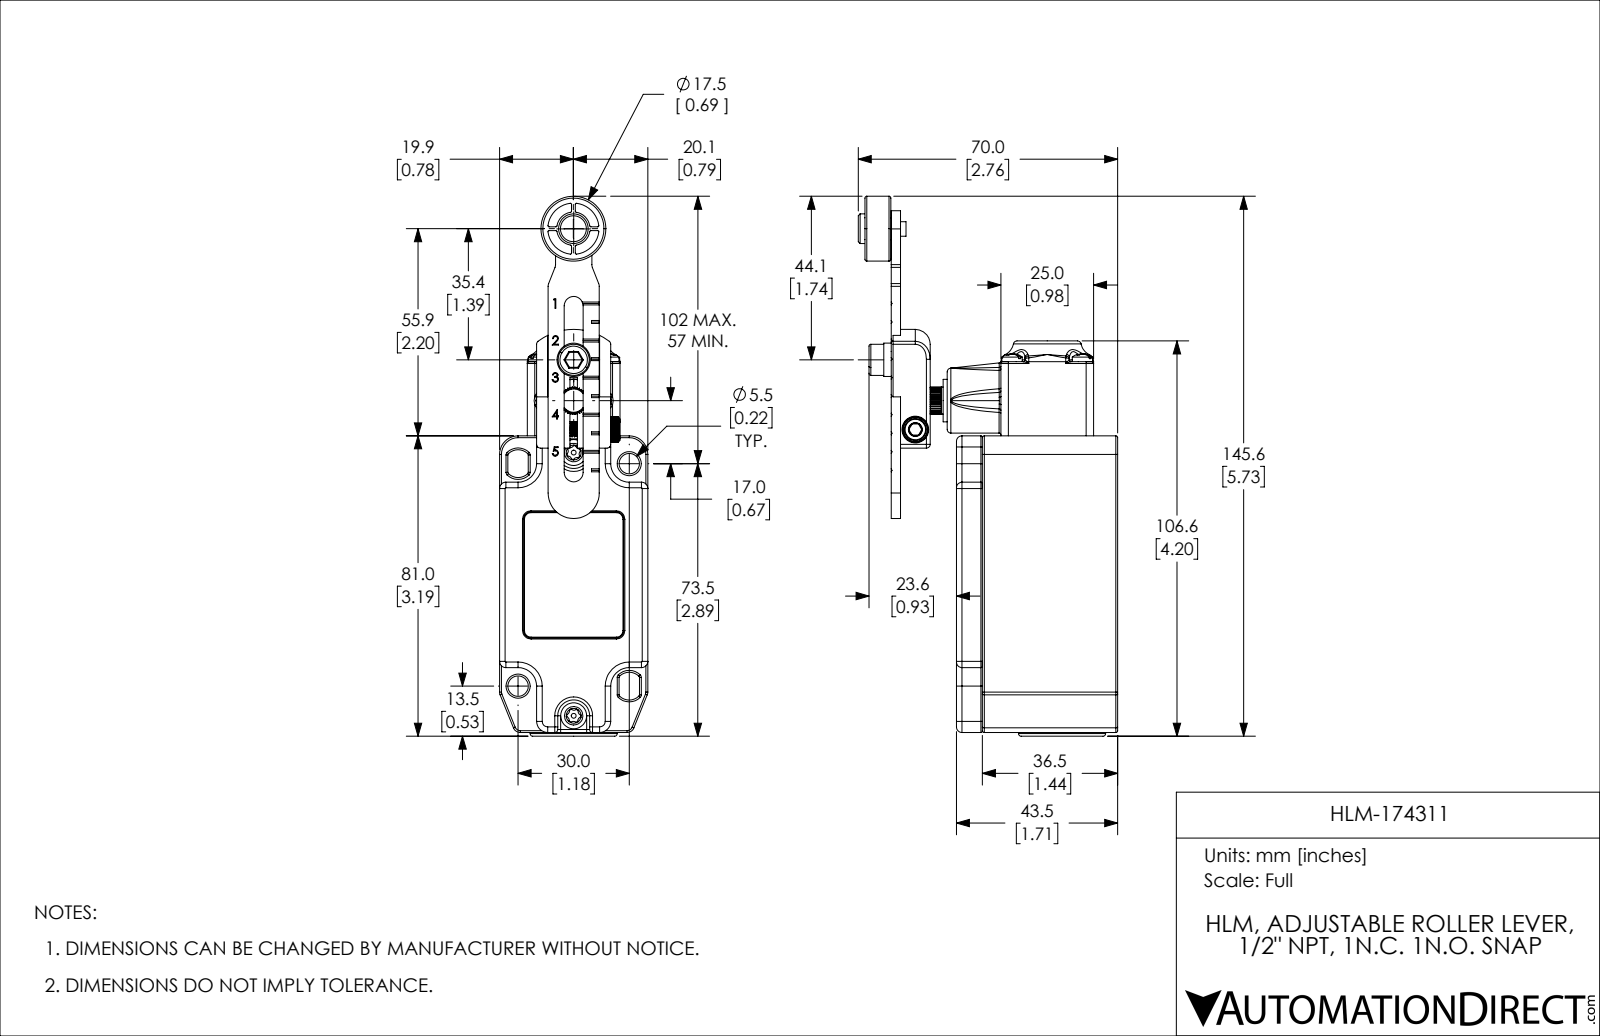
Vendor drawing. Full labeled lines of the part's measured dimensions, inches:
Part name (STEP PRODUCT): 174-HLM (Adjustable Roller Lever) (STEP format)
STEP written by: SolidWorks 2015 (CONFIG_CONTROL_DESIGN)
Units: inches
Bodies: 19 solids, 3642 faces (1059 planar, 954 cylindrical, 1629 other)
Overall size (bounding box): 5.733 × 2.756 × 1.575
Volume: 4.562 in³ · Surface area: 86.23 in²
Round holes (diameter × count): ⌀0.118 ×10, ⌀0.106 ×4, ⌀0.134 ×4, ⌀0.161 ×3, ⌀0.146 ×2, ⌀0.15 ×2, ⌀0.157 ×2, ⌀0.165 ×2, ⌀0.217 ×2, ⌀0.571 ×2, ⌀0.114 ×1, ⌀0.126 ×1
Round bosses / shafts (diameter × count): ⌀0.244 ×6, ⌀0.216 ×4, ⌀0.252 ×3, ⌀0.689 ×2, ⌀0.354 ×2, ⌀0.276 ×2, ⌀0.154 ×2, ⌀0.051 ×2
Partial cylindrical surfaces — rounded edges, fillets, slot ends (radius × count): R0.02 ×166, R0.012 ×44, R0.039 ×40, R0.016 ×26, R0.079 ×16, R0.006 ×14, R0.031 ×10, R0.059 ×9
Main face-to-face distances: 0.089, 0.098, 1.486, 1.575, 2.307, 1.398, 0.102, 1.512, 0.697, 1.61
Hole centre spacings: 0.748, 0.529, 1.258, 0.354, 0.432, 0.65, 0.75, 0.828
